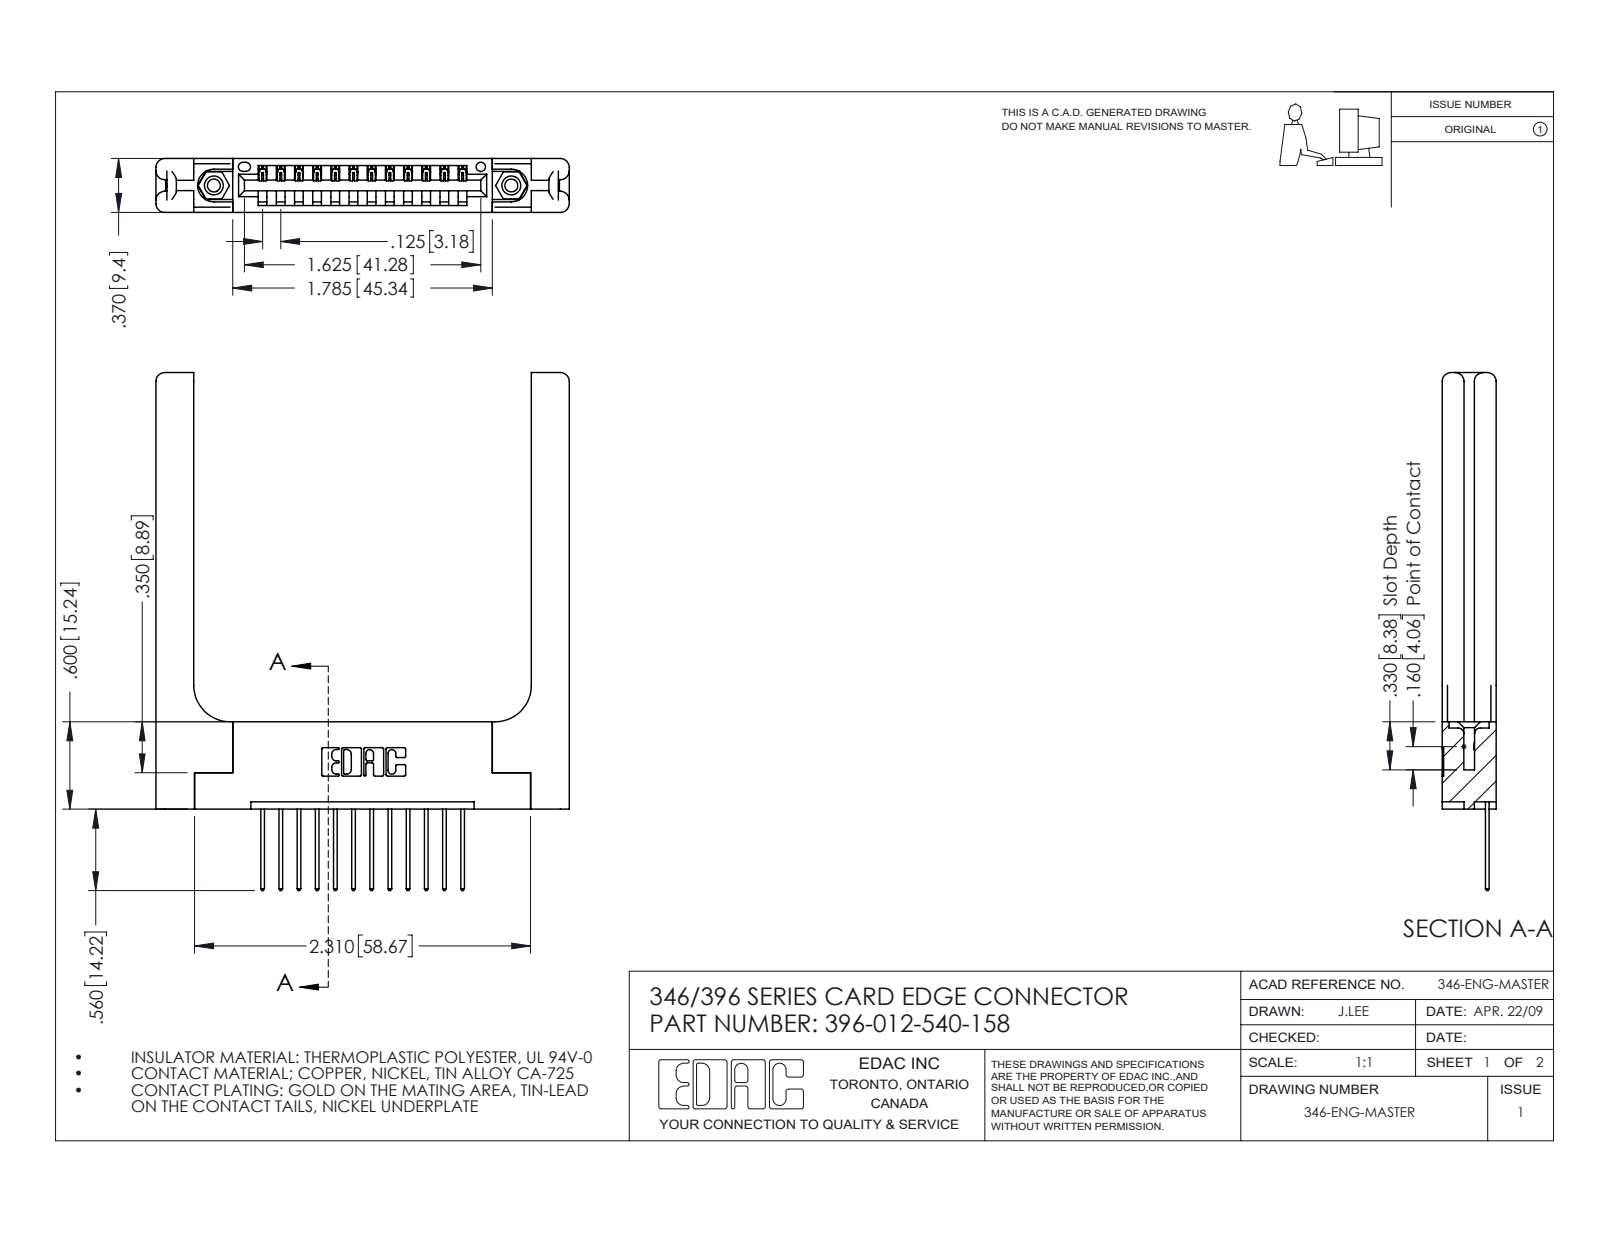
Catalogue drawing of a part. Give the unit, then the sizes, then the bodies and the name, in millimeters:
Units: millimetres
Overall size (bounding box): 90.4 × 72.2 × 9.4
Round holes (diameter × count): ⌀2.3 ×2, ⌀3.2 ×2, ⌀4 ×2, ⌀1.6 ×1
Round bosses / shafts (diameter × count): ⌀3.9 ×2
Partial cylindrical surfaces — rounded edges, fillets, slot ends (radius × count): R0.2 ×24, R0.3 ×24, R0.3 ×22, R1.5 ×16, R0.2 ×6, R0.8 ×6, R0.7 ×3, R0.8 ×2
Main face-to-face distances: 9.4, 3.8, 1.8, 3.8, 1.2, 8.2, 5.6, 6.4, 2.6, 4.4
Hole centre spacings: 6.2, 46.7, 51.9
Volume: 14 200 mm³ · Surface area: 13 360 mm²
Bodies: 17 solids, 1074 faces (704 planar, 310 cylindrical, 60 other)
Part name (STEP PRODUCT): 345-292-001_345-293-140; 345-250-001_345-250-001-102; 346-220-058_345-220-058; 396-012-540-158 (+1 more)
STEP written by: SolidWorks 2016 (CONFIG_CONTROL_DESIGN)
